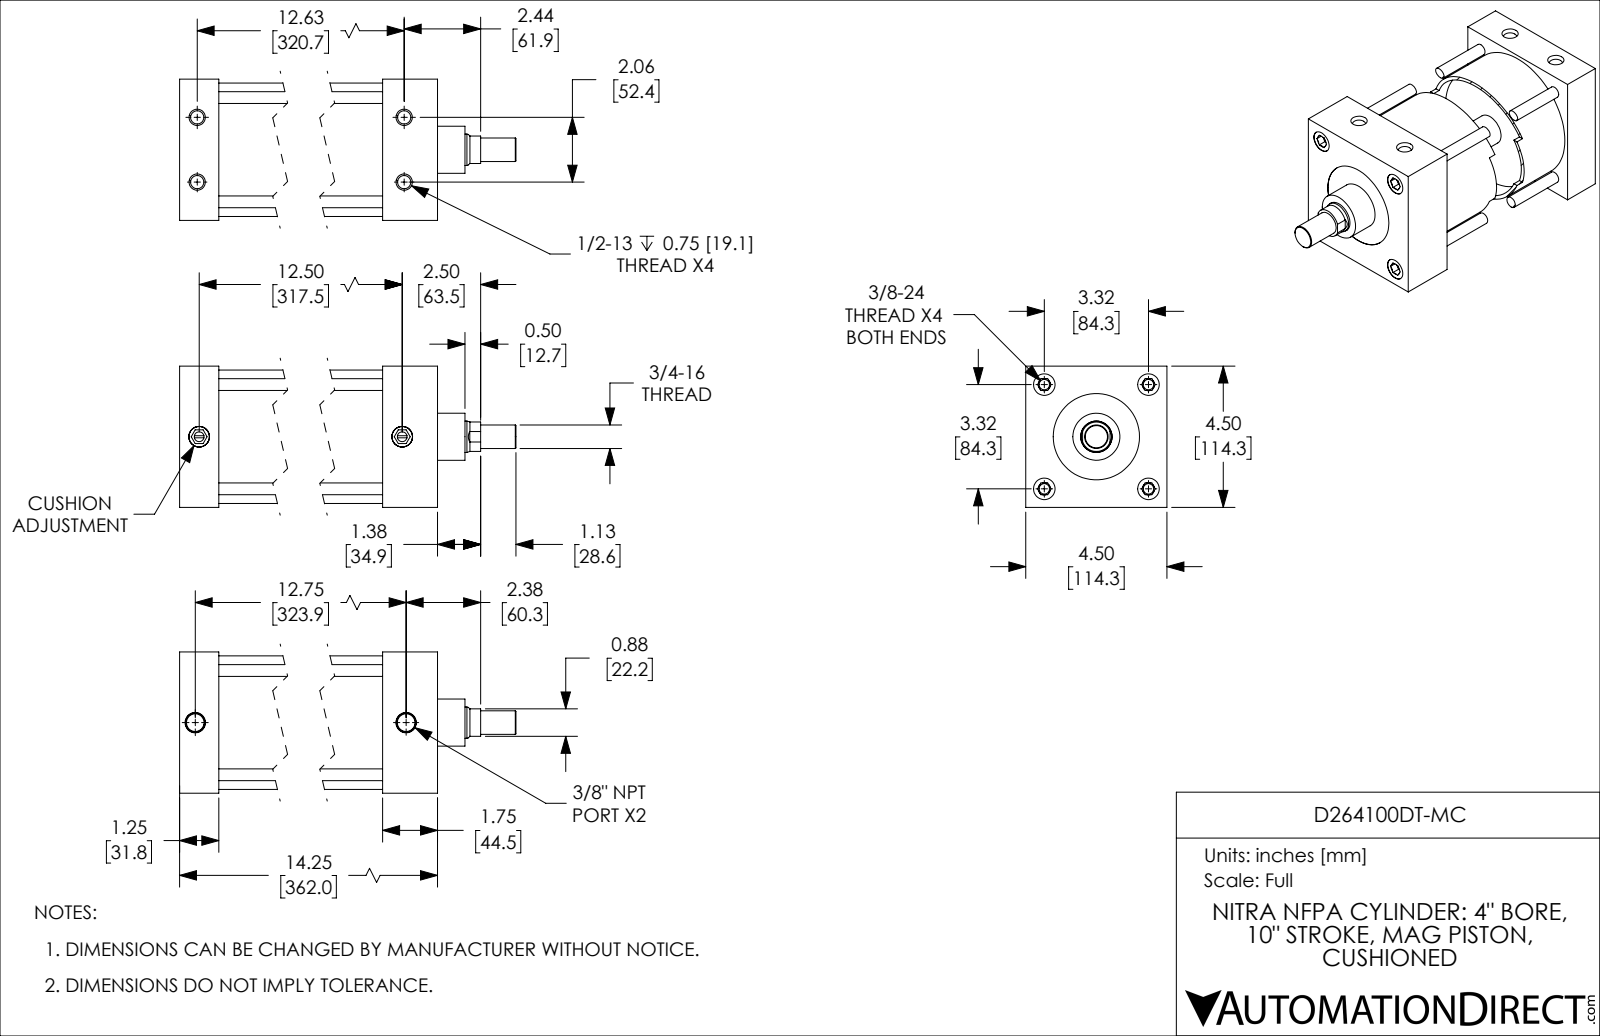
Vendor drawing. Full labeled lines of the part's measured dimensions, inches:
Part name (STEP PRODUCT): D264100DT-MC_CUSHION; D264100DT-MC_PISTON_KK1; D264100DT-MC; D264100DT-MC_BODY
STEP written by: SolidWorks 2019 (CONFIG_CONTROL_DESIGN)
Units: inches
Bodies: 4 solids, 246 faces (90 planar, 78 cylindrical, 78 other)
Overall size (bounding box): 16.75 × 4.5 × 4.5
Volume: 107.4 in³ · Surface area: 594.5 in²
Round holes (diameter × count): ⌀0.332 ×4, ⌀0.422 ×4, ⌀0.687 ×4, ⌀0.312 ×2, ⌀0.562 ×2, ⌀0.656 ×2, ⌀1.001 ×1, ⌀2.75 ×1, ⌀4.001 ×1
Round bosses / shafts (diameter × count): ⌀0.375 ×4, ⌀0.657 ×2, ⌀4.251 ×1, ⌀3.999 ×1, ⌀1.5 ×1, ⌀0.999 ×1, ⌀0.75 ×1
Partial cylindrical surfaces — rounded edges, fillets, slot ends (radius × count): R0.469 ×1
Main face-to-face distances: 1.25, 4.5, 12.5, 11.25, 14.25, 13, 1.75, 2.5, 10, 11.75
Hole centre spacings: 1.033, 2.347, 3.32, 12.729, 2.062, 4.695, 12.625, 12.792
